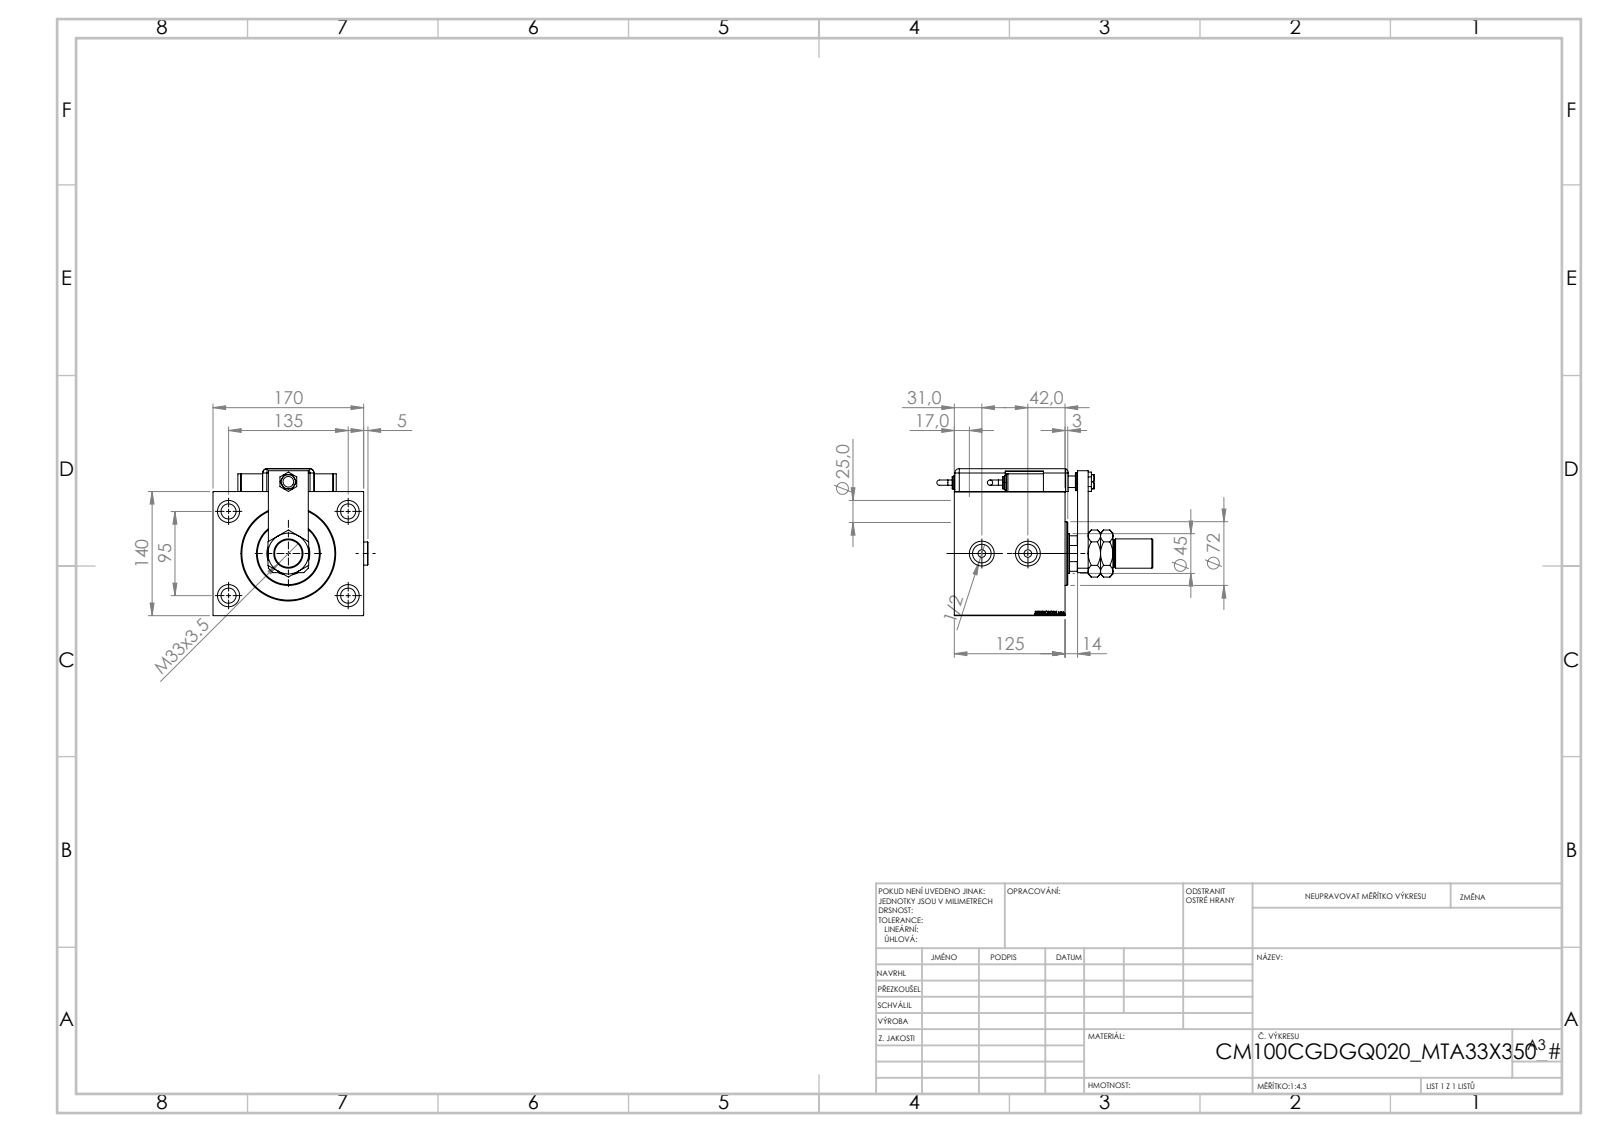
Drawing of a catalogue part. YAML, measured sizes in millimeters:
part_name: "Zatka_OIL_PORT; MAGNETIC SWITCH Q; SWITCH Q; SWITCH DIM A_G (+7 more)"
step_written_by: "SolidWorks 2019 (CONFIG_CONTROL_DESIGN)"
units: millimeters
bodies: {solids: 16, faces: 1350, planar: 664, cylindrical: 135, other: 551}
overall_size: [243.76, 174.9, 165.8]
volume: 3012000
surface_area: 318859
round_holes:
  - {diameter: 17, count: 4}
  - {diameter: 25, count: 4}
  - {diameter: 4, count: 2}
  - {diameter: 8, count: 2}
  - {diameter: 8.5, count: 2}
  - {diameter: 20.96, count: 2}
  - {diameter: 28, count: 2}
  - {diameter: 12, count: 1}
  - {diameter: 13, count: 1}
  - {diameter: 14, count: 1}
  - {diameter: 31.5, count: 1}
  - {diameter: 33, count: 1}
round_bosses_or_shafts:
  - {diameter: 20, count: 3}
  - {diameter: 26, count: 2}
  - {diameter: 16, count: 2}
  - {diameter: 14, count: 2}
  - {diameter: 6, count: 2}
  - {diameter: 72, count: 1}
  - {diameter: 31, count: 1}
partial_cylinders:
  - {radius: 5, count: 9}
  - {radius: 10, count: 1}
  - {radius: 22, count: 1}
face_to_face_distances: [140, 125, 51, 170, 74, 3, 10, 77, 21.6, 29.4]
hole_center_spacings: [82.54, 75.36, 95, 135, 145.15, 165.08, 20, 52]
